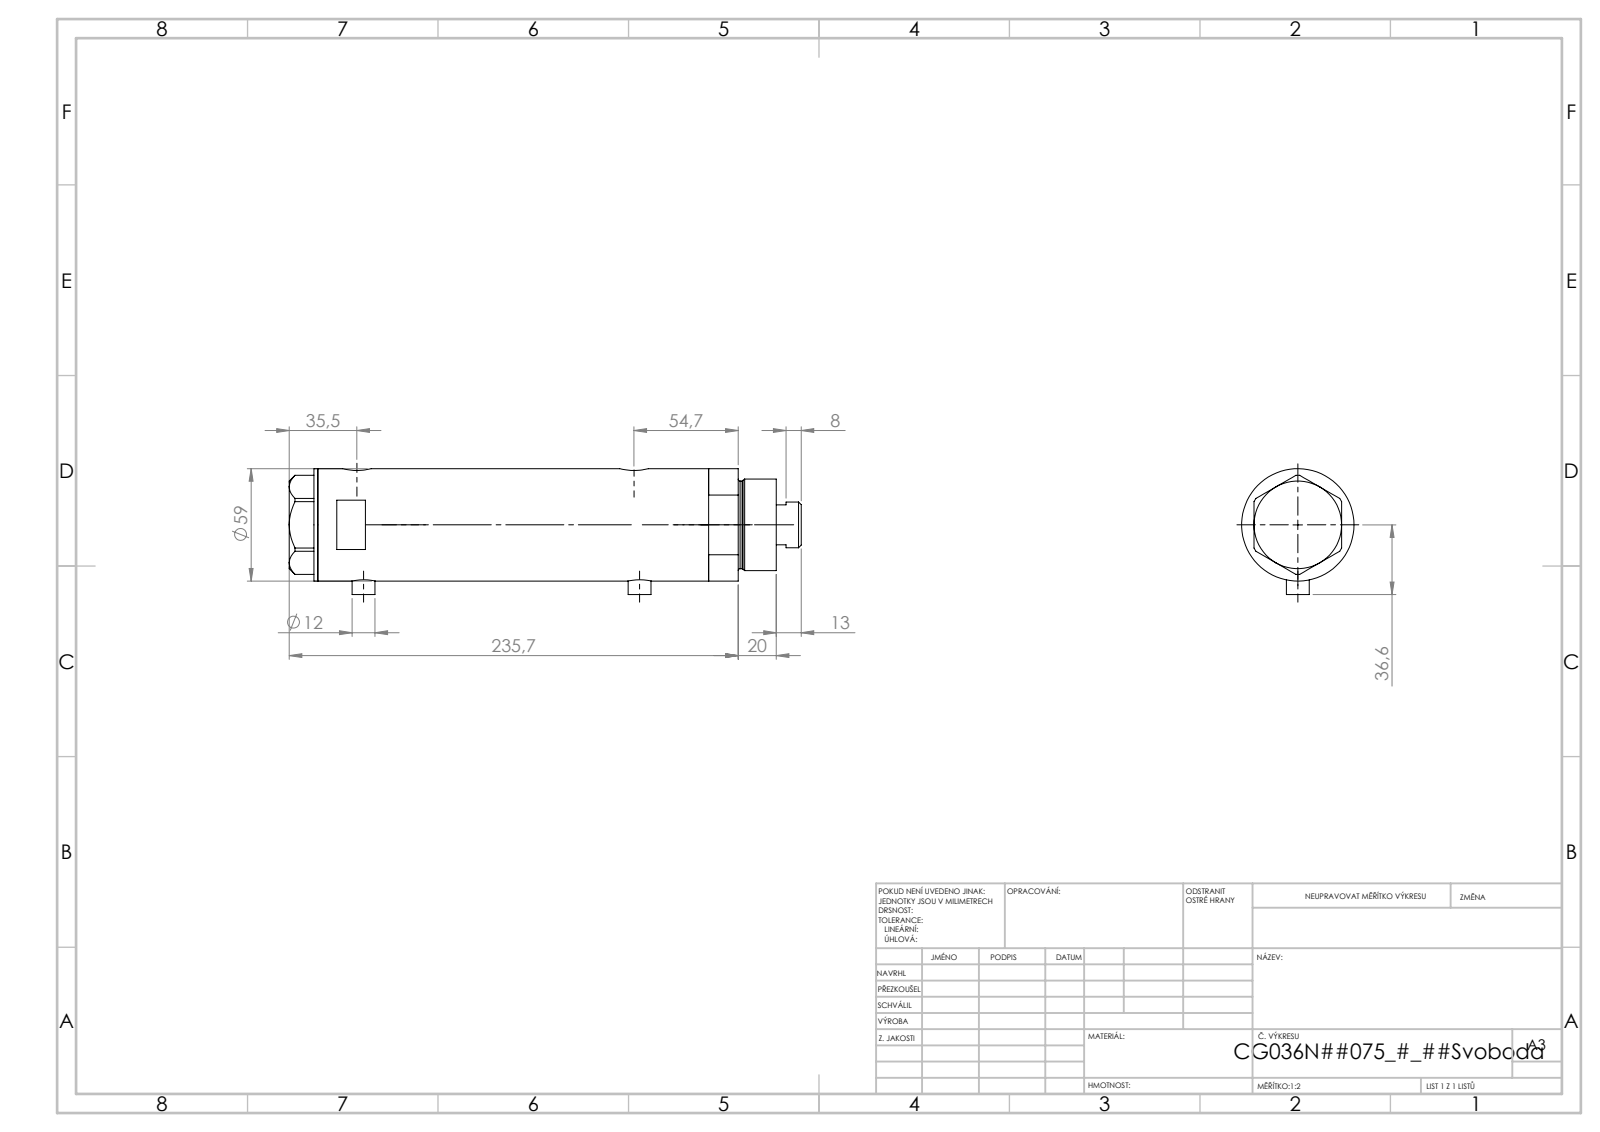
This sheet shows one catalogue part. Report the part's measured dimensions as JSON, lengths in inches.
{"part_name": "V270CG_VC; V270CG_BACK; V270CG_FRONT; V270CG_MIDDLE", "step_written_by": "SolidWorks 2019 (CONFIG_CONTROL_DESIGN)", "units": "inches", "bodies": {"solids": 4, "faces": 126, "planar": 53, "cylindrical": 53, "other": 20}, "overall_size": [10.583, 2.602, 2.323], "volume_in3": 38.23, "surface_area_in2": 192.4, "round_holes": [[0.197, 2], [0.383, 2], [0.492, 2], [0.591, 2], [0.335, 1], [0.984, 1], [1.043, 1], [1.417, 1], [1.575, 1], [2.047, 1]], "round_bosses_or_shafts": [[0.472, 2], [2.323, 1], [1.89, 1], [1.811, 1], [0.945, 1]], "face_to_face_distances": [6.583, 0.925, 5.657, 0.591, 1.516, 7.173, 0.079, 9.476, 10.067, 8.551], "hole_center_spacings": [0.114, 0.138, 5.591, 5.705, 5.728, 5.843]}
